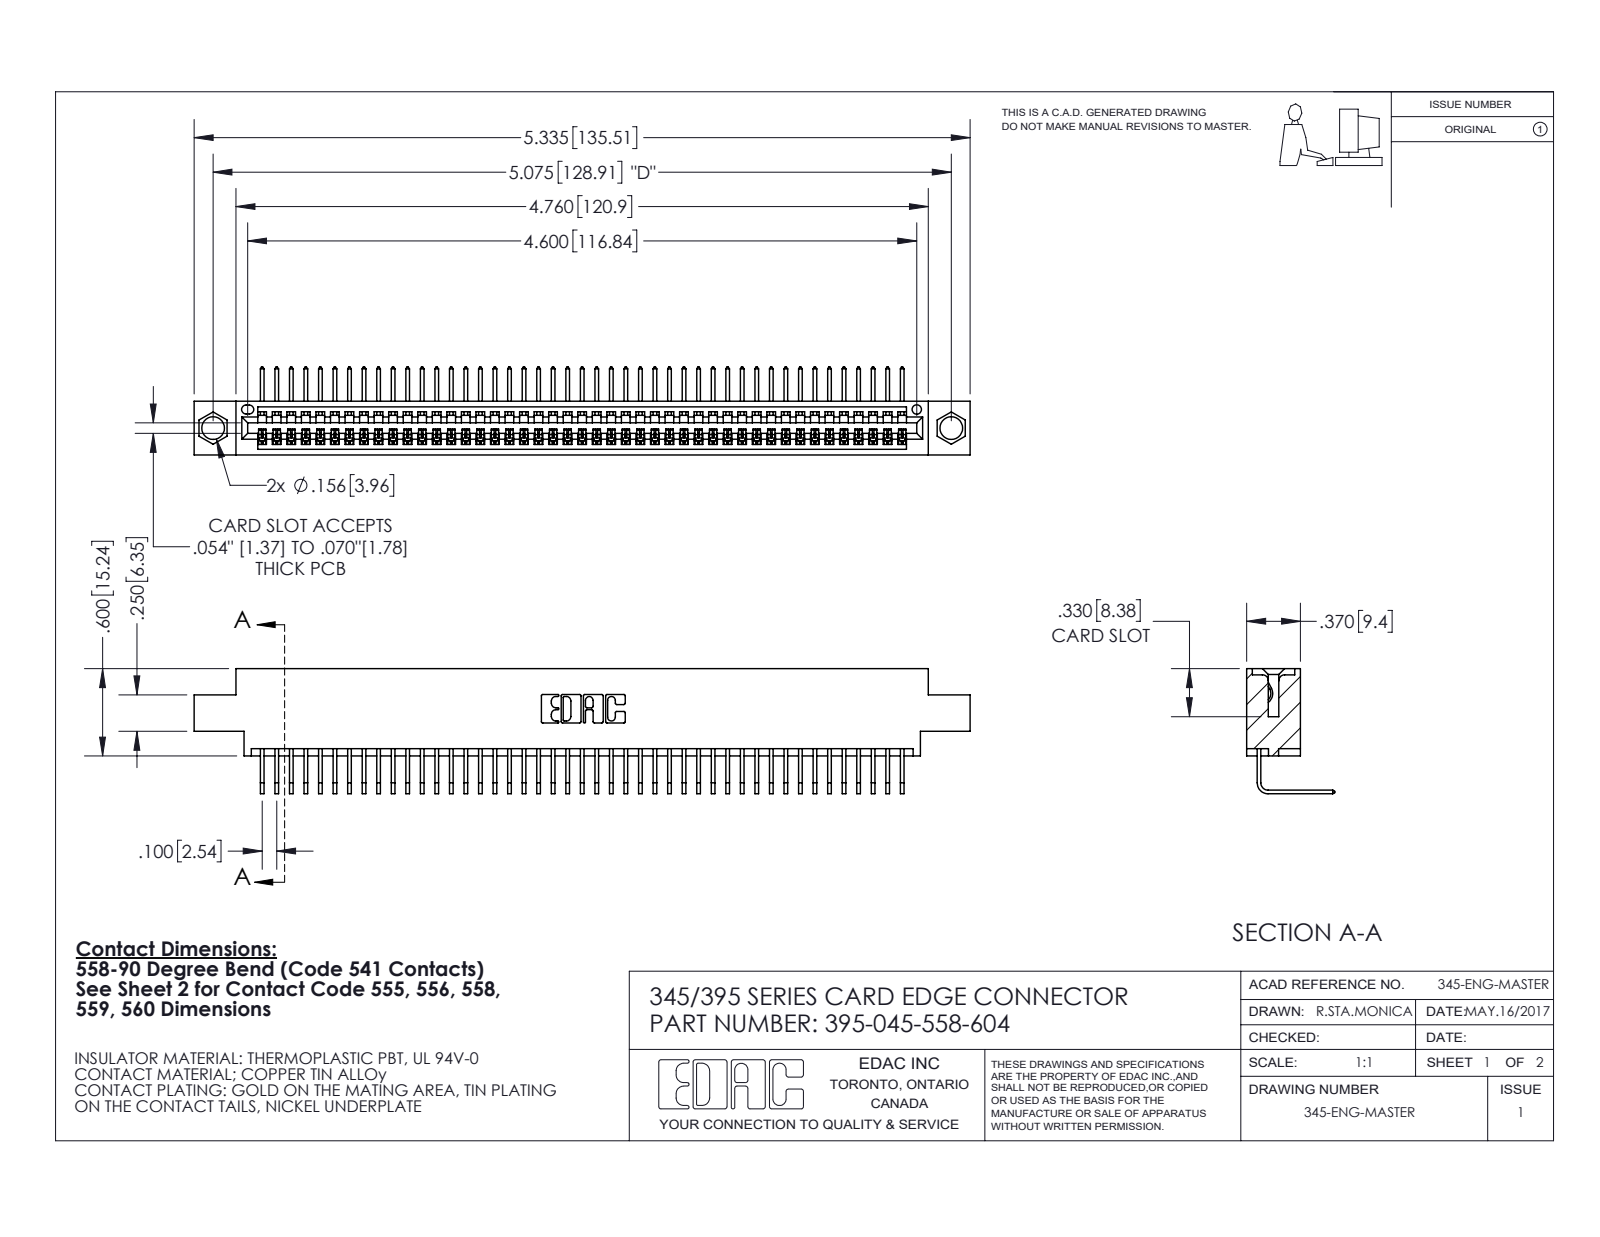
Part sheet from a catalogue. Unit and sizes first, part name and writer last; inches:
Units: inches
Overall size (bounding box): 5.335 × 0.859 × 0.605
Round holes (diameter × count): ⌀0.156 ×2, ⌀0.064 ×1
Partial cylindrical surfaces — rounded edges, fillets, slot ends (radius × count): R0.006 ×90, R0.01 ×22, R0.007 ×6, R0.031 ×6, R0.026 ×3, R0.031 ×2, R0.04 ×2, R0.014 ×1
Main face-to-face distances: 0.072, 0.298, 0.37, 0.2, 0.098, 0.272, 0.025, 0.225, 0.175, 0.149
Hole centre spacings: 0.27, 4.839, 5.075
Volume: 0.783 in³ · Surface area: 27.8 in²
Bodies: 46 solids, 2844 faces (1988 planar, 856 cylindrical, 0 other)
Part name (STEP PRODUCT): 345 Part_0.170 Offset - 0.156 Dia-TI; 395-045-558-604; 345-292-001_558 Tail - 2
STEP written by: SolidWorks 2020 (CONFIG_CONTROL_DESIGN)
